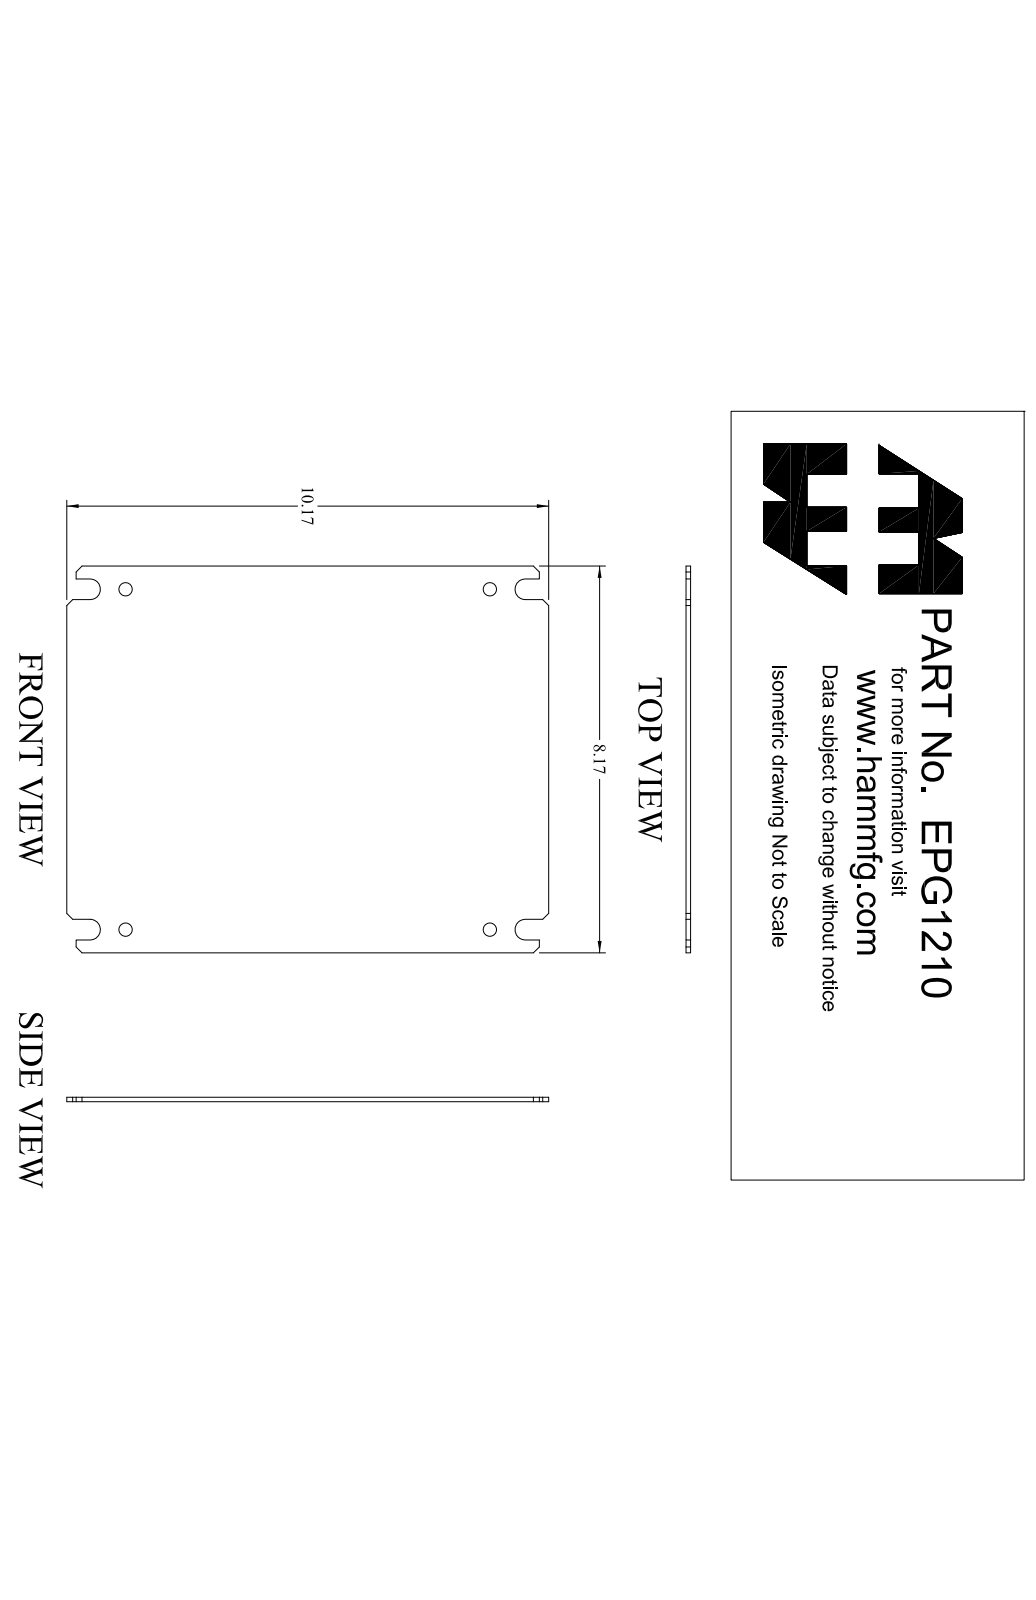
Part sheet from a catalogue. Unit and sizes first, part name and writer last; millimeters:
Units: millimetres
Overall size (bounding box): 258.3 × 207.5 × 2.4
Round holes (diameter × count): ⌀7.1 ×4
Partial cylindrical surfaces — rounded edges, fillets, slot ends (radius × count): R5.6 ×4
Main face-to-face distances: 2.4, 207.5, 258.3, 18, 189.5, 6.9, 200.6, 11.1, 182.6, 171.5
Hole centre spacings: 182.6, 195.3, 267.3
Volume: 126 700 mm³ · Surface area: 107 700 mm²
Bodies: 1 solid, 40 faces (26 planar, 14 cylindrical, 0 other)
Part name (STEP PRODUCT): EPG1210
STEP written by: SolidWorks 2018 (AUTOMOTIVE_DESIGN)
